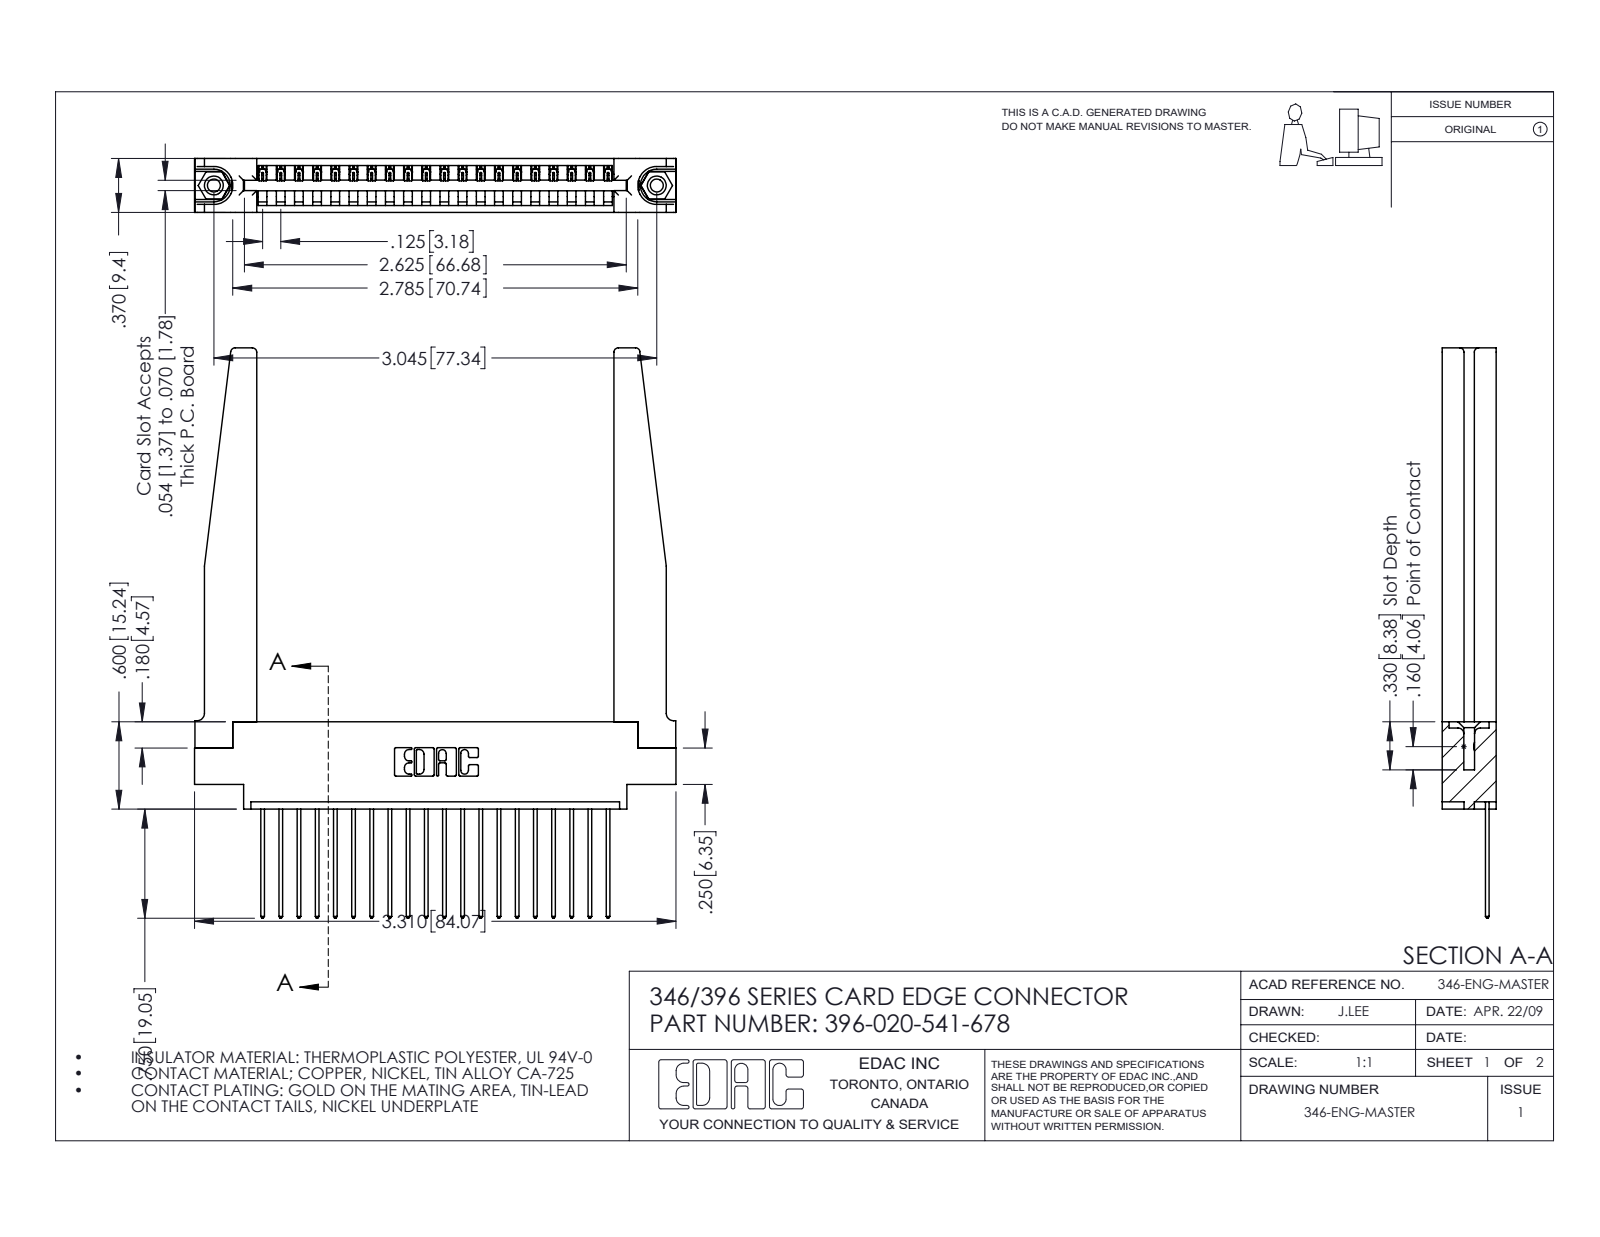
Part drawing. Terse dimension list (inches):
name: 346 Part_0.170 Offset - 0.156 Dia-TH; 396-020-541-678; 345-250-001_345-250-001-102; 346-220-078_345-220-078 (+1 more)
written by: SolidWorks 2016 (CONFIG_CONTROL_DESIGN)
unit: in
bodies: 25 solids, 1520 faces (1022 planar, 446 cylindrical, 52 other)
size: 3.92 × 3.31 × 0.37
volume: 0.898 in³; area: 25.75 in²
holes: 2× ⌀0.089, 2× ⌀0.125, 2× ⌀0.156, 1× ⌀0.064
bosses: 2× ⌀0.155
rounds: 40× R0.006, 40× R0.01, 22× R0.01, 8× R0.03, 6× R0.007, 6× R0.031, 3× R0.026, 2× R0.031
face distances: 0.37, 0.072, 0.048, 0.322, 0.15, 0.148, 0.25, 0.298, 0.025, 0.102
hole spacings: 0.246, 2.837, 3.045
